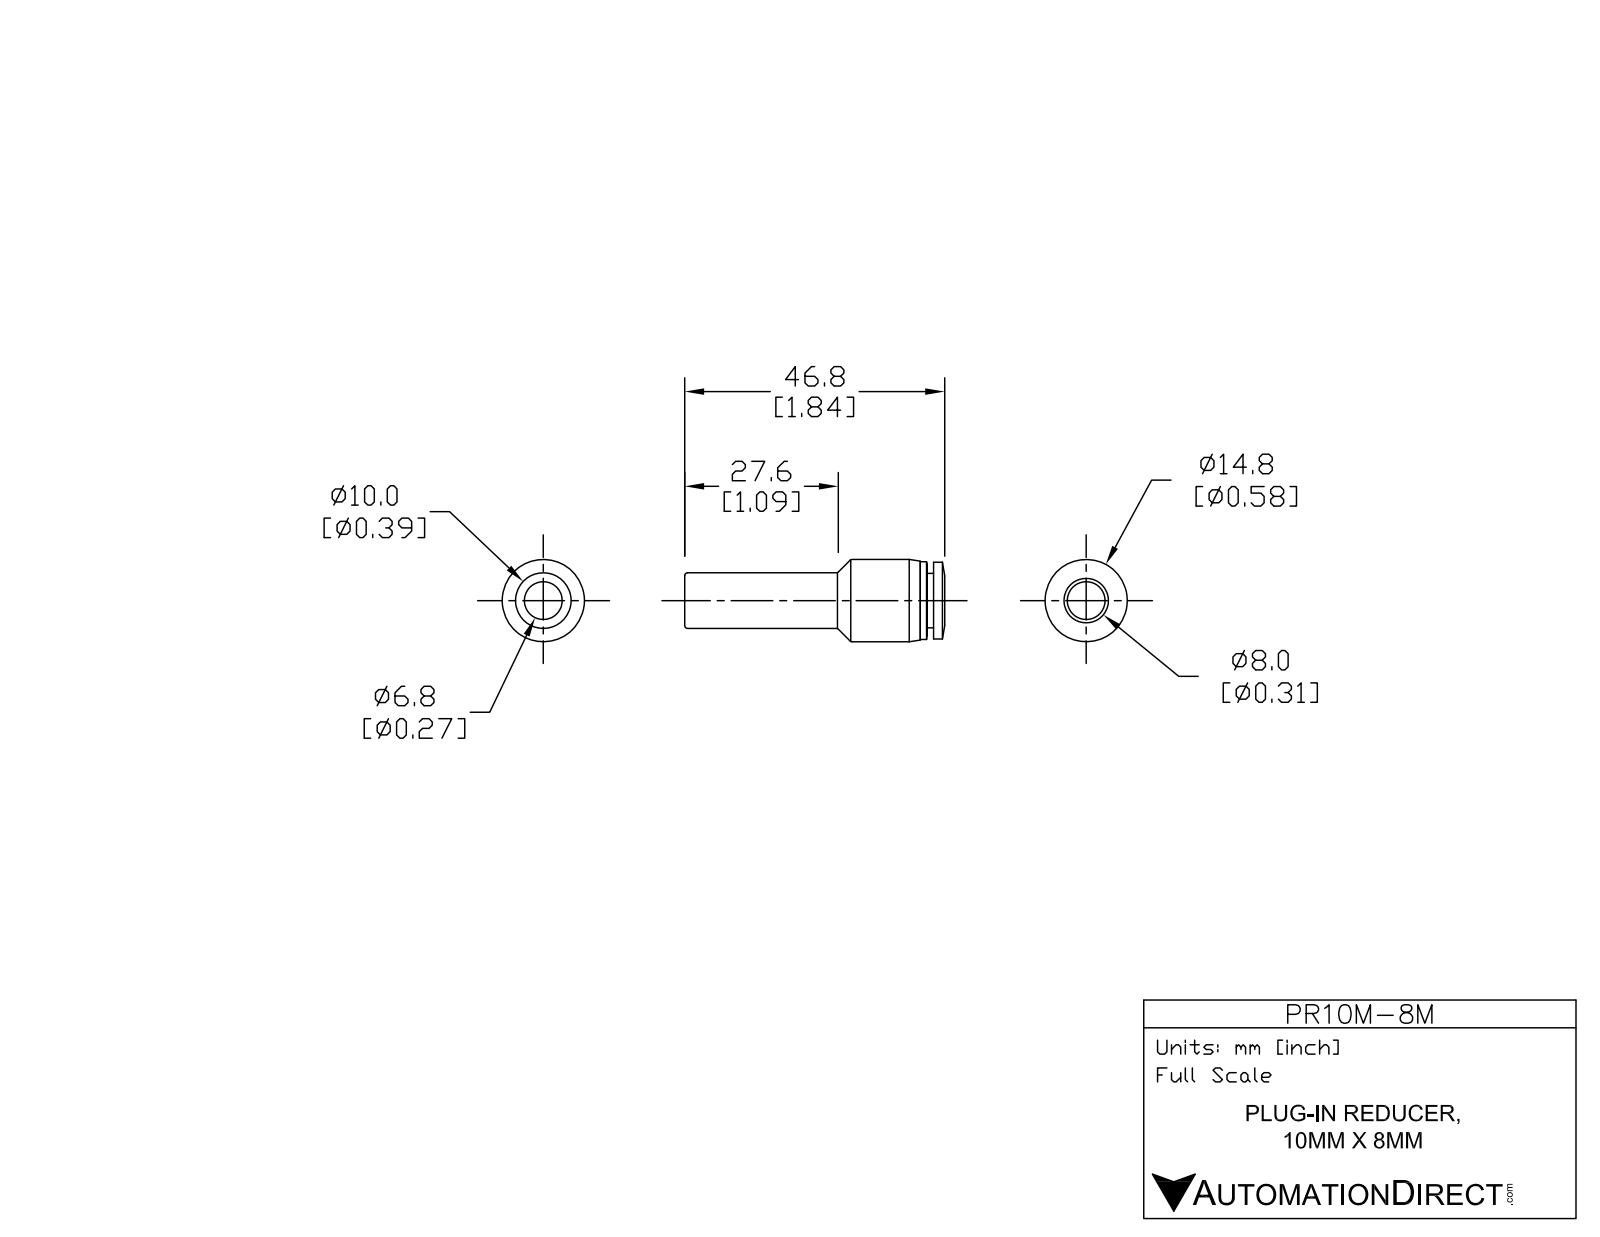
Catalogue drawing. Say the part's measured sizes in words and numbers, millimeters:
The part is named "PR10M-8M". Its 3-D file was written by "SolidWorks 2015 (AUTOMOTIVE_DESIGN)". It is 1 solid with 36 faces: 6 planar, 14 cylindrical and 16 other. Overall it measures 46.7 by 14.8 by 14.8 millimeters. Its volume is 3 060 cubic millimeters and its surface area 3 103 square millimeters. Round holes: 1 of diameter 6.8, 1 of diameter 8.3. Round bosses or shafts: 1 of diameter 14.8, 1 of diameter 14, 1 of diameter 13.8, 1 of diameter 10, 1 of diameter 9.8. The main face-to-face distances are 1.4, 43.3, 44.7, 28.3, 14.9, 16.3, 46.7, 18.3, 3.4, 2.
